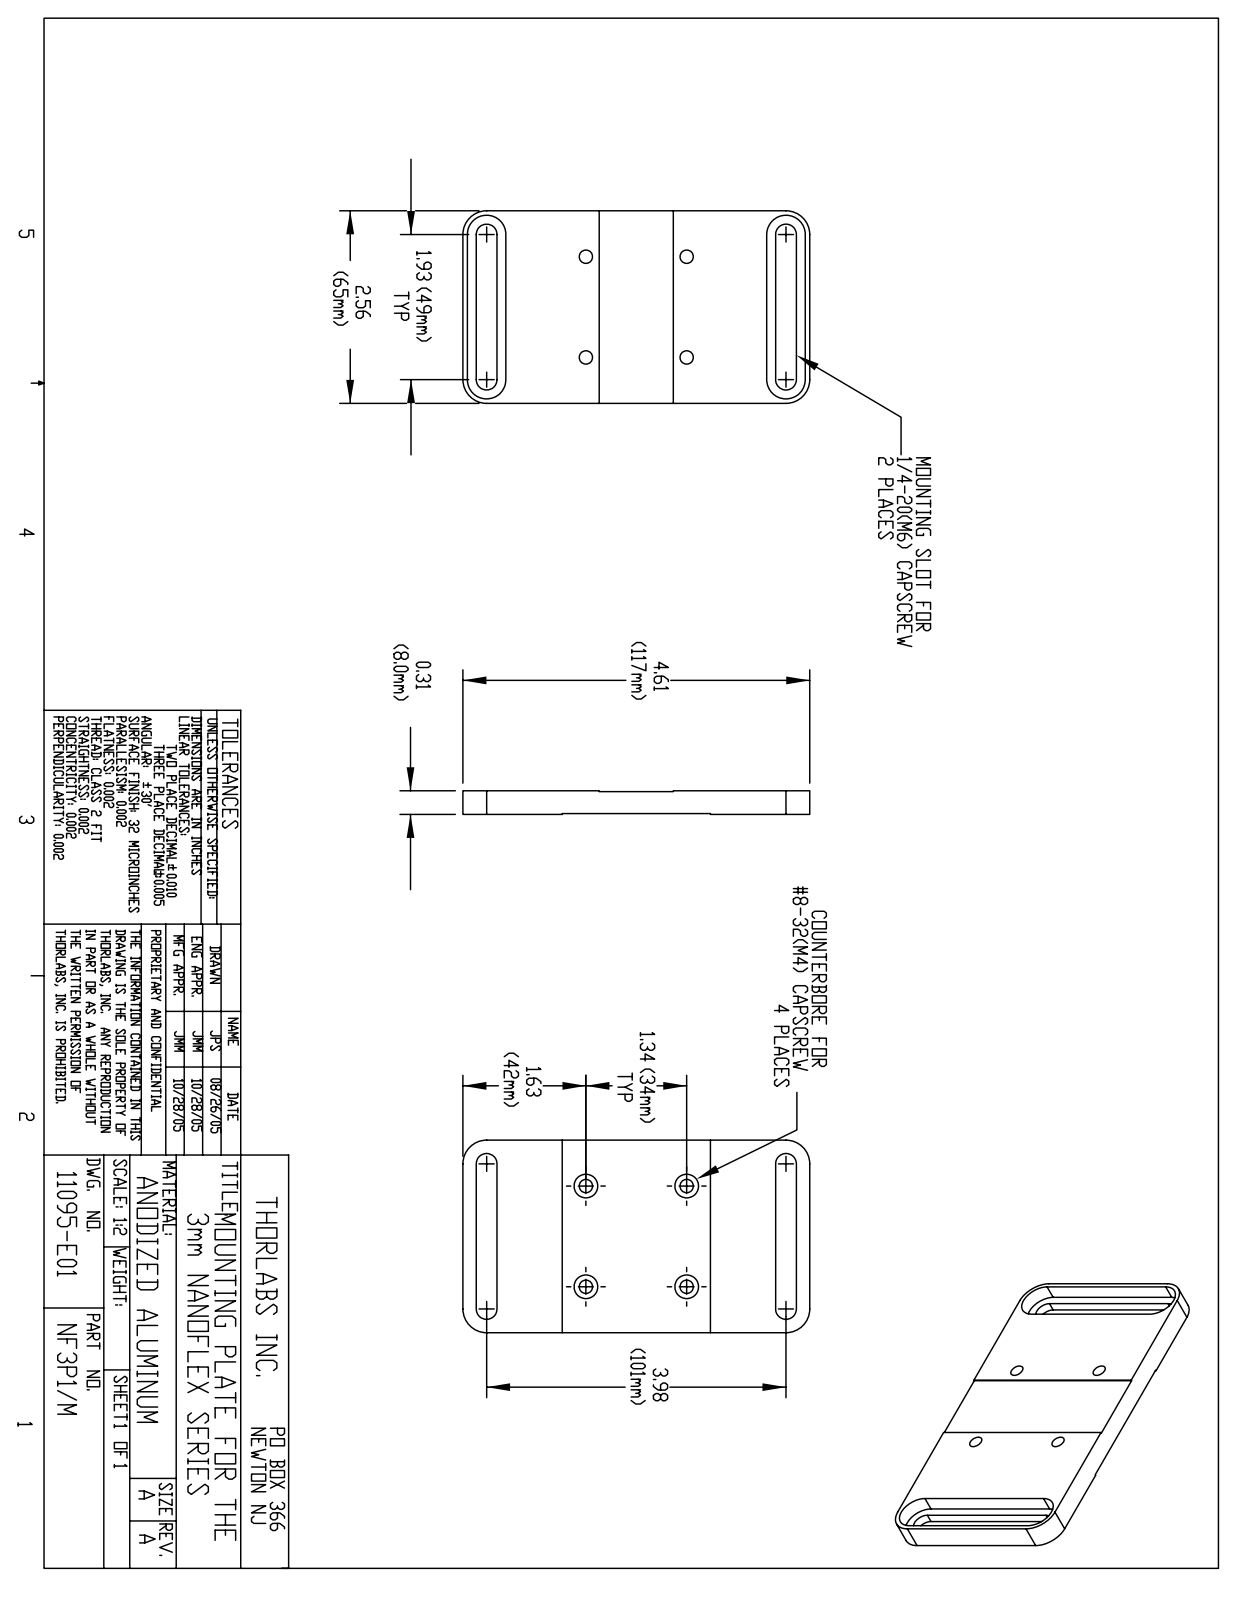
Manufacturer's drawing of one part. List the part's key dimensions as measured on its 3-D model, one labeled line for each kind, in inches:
Part name (STEP PRODUCT): 11095-E0W
STEP written by: SolidWorks 2007 (AUTOMOTIVE_DESIGN)
Units: inches
Bodies: 0 solids, 83 faces (47 planar, 32 cylindrical, 4 other)
Overall size (bounding box): 4.606 × 2.563 × 0.315
Round holes (diameter × count): ⌀0.177 ×4, ⌀0.315 ×4
Partial cylindrical surfaces — rounded edges, fillets, slot ends (radius × count): R0.138 ×4, R0.256 ×4, R0.315 ×4
Main face-to-face distances: 0.303, 0.315, 0.291, 0.118, 2.559, 3.976, 0.106, 0.185, 0.197, 0.394
Hole centre spacings: 1.339, 1.893
